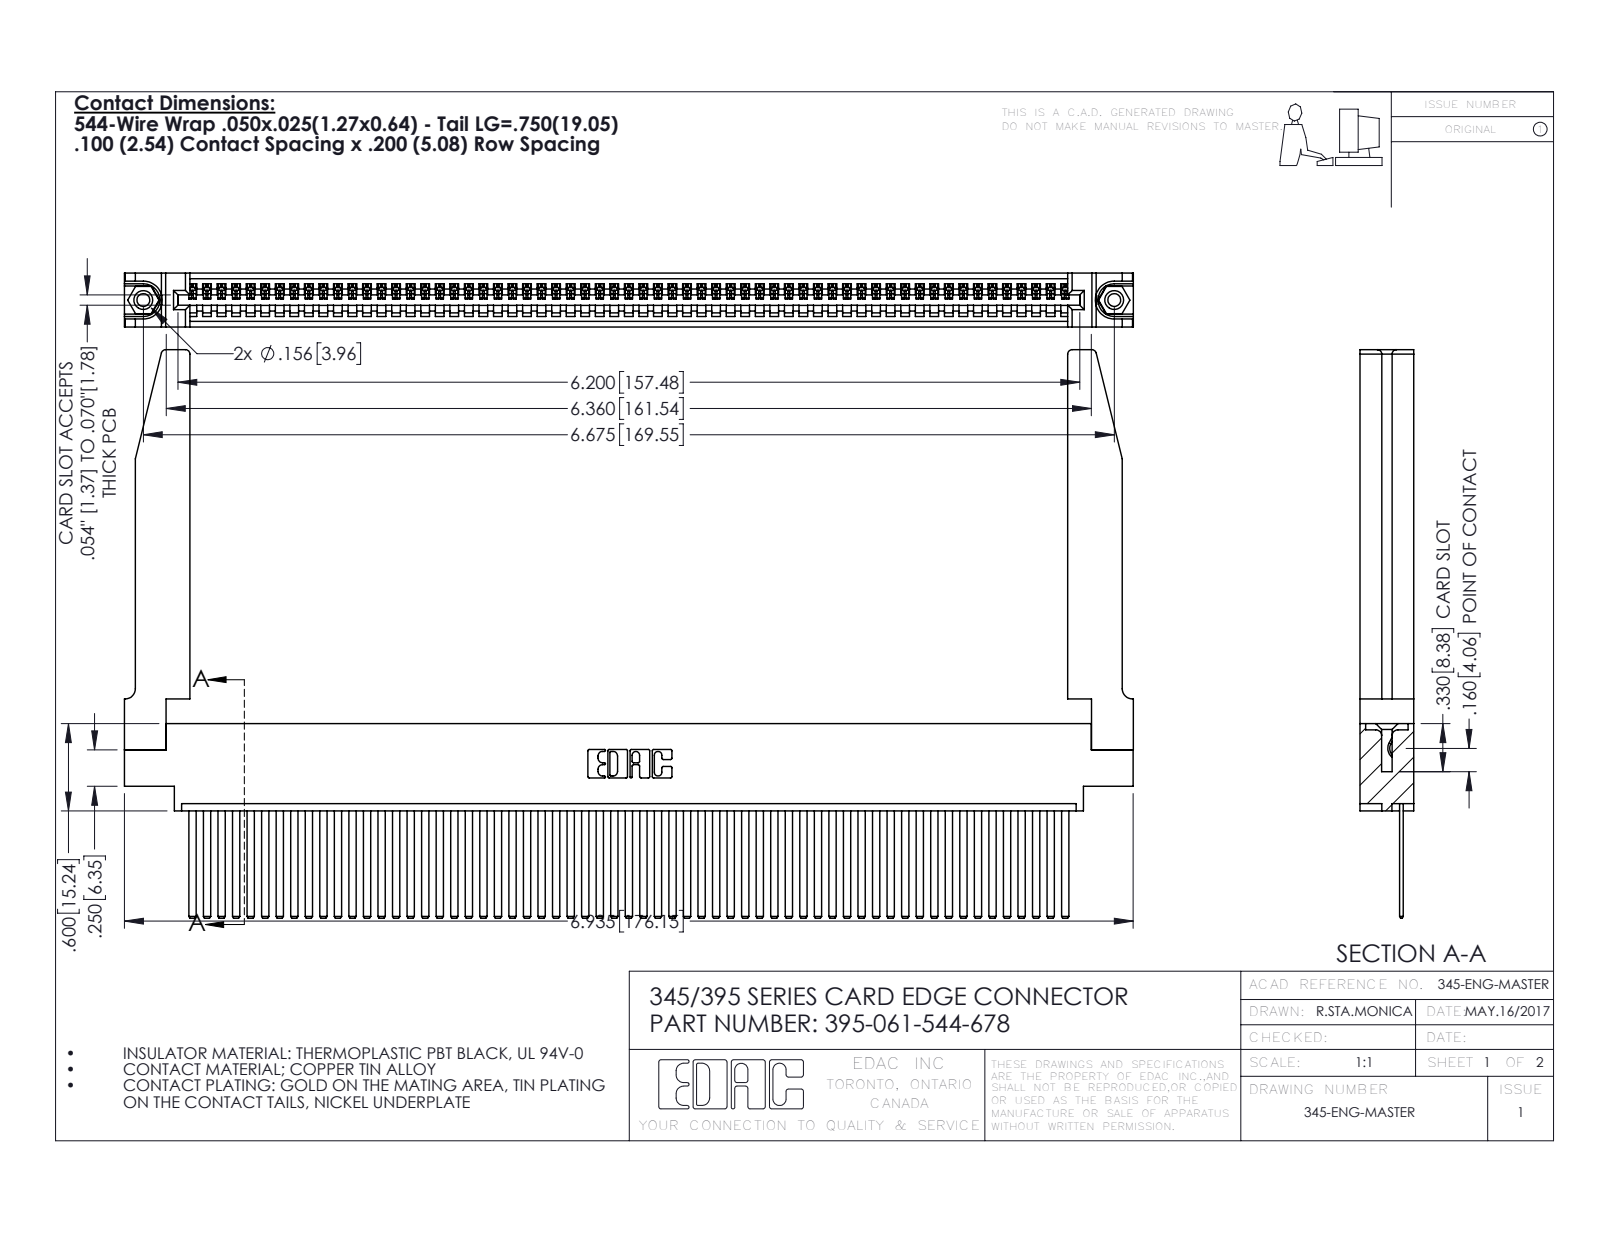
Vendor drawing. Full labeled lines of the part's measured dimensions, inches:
Part name (STEP PRODUCT): 345-220-078_345-220-078; 395-061-544-678; 345-292-001_345-293-144; 345-250-001_345-250-001-102 (+1 more)
STEP written by: SolidWorks 2016 (CONFIG_CONTROL_DESIGN)
Units: inches
Bodies: 66 solids, 3536 faces (2422 planar, 1062 cylindrical, 52 other)
Overall size (bounding box): 6.936 × 3.907 × 0.37
Volume: 1.541 in³ · Surface area: 50.5 in²
Round holes (diameter × count): ⌀0.089 ×2, ⌀0.125 ×2, ⌀0.156 ×2, ⌀0.064 ×1
Round bosses / shafts (diameter × count): ⌀0.155 ×2
Partial cylindrical surfaces — rounded edges, fillets, slot ends (radius × count): R0.006 ×122, R0.01 ×22, R0.03 ×8, R0.007 ×6, R0.031 ×6, R0.026 ×3, R0.031 ×2, R0.04 ×2
Main face-to-face distances: 0.072, 0.298, 0.37, 0.098, 0.272, 0.025, 0.2, 0.225, 0.148, 0.15
Hole centre spacings: 0.27, 6.439, 6.675
